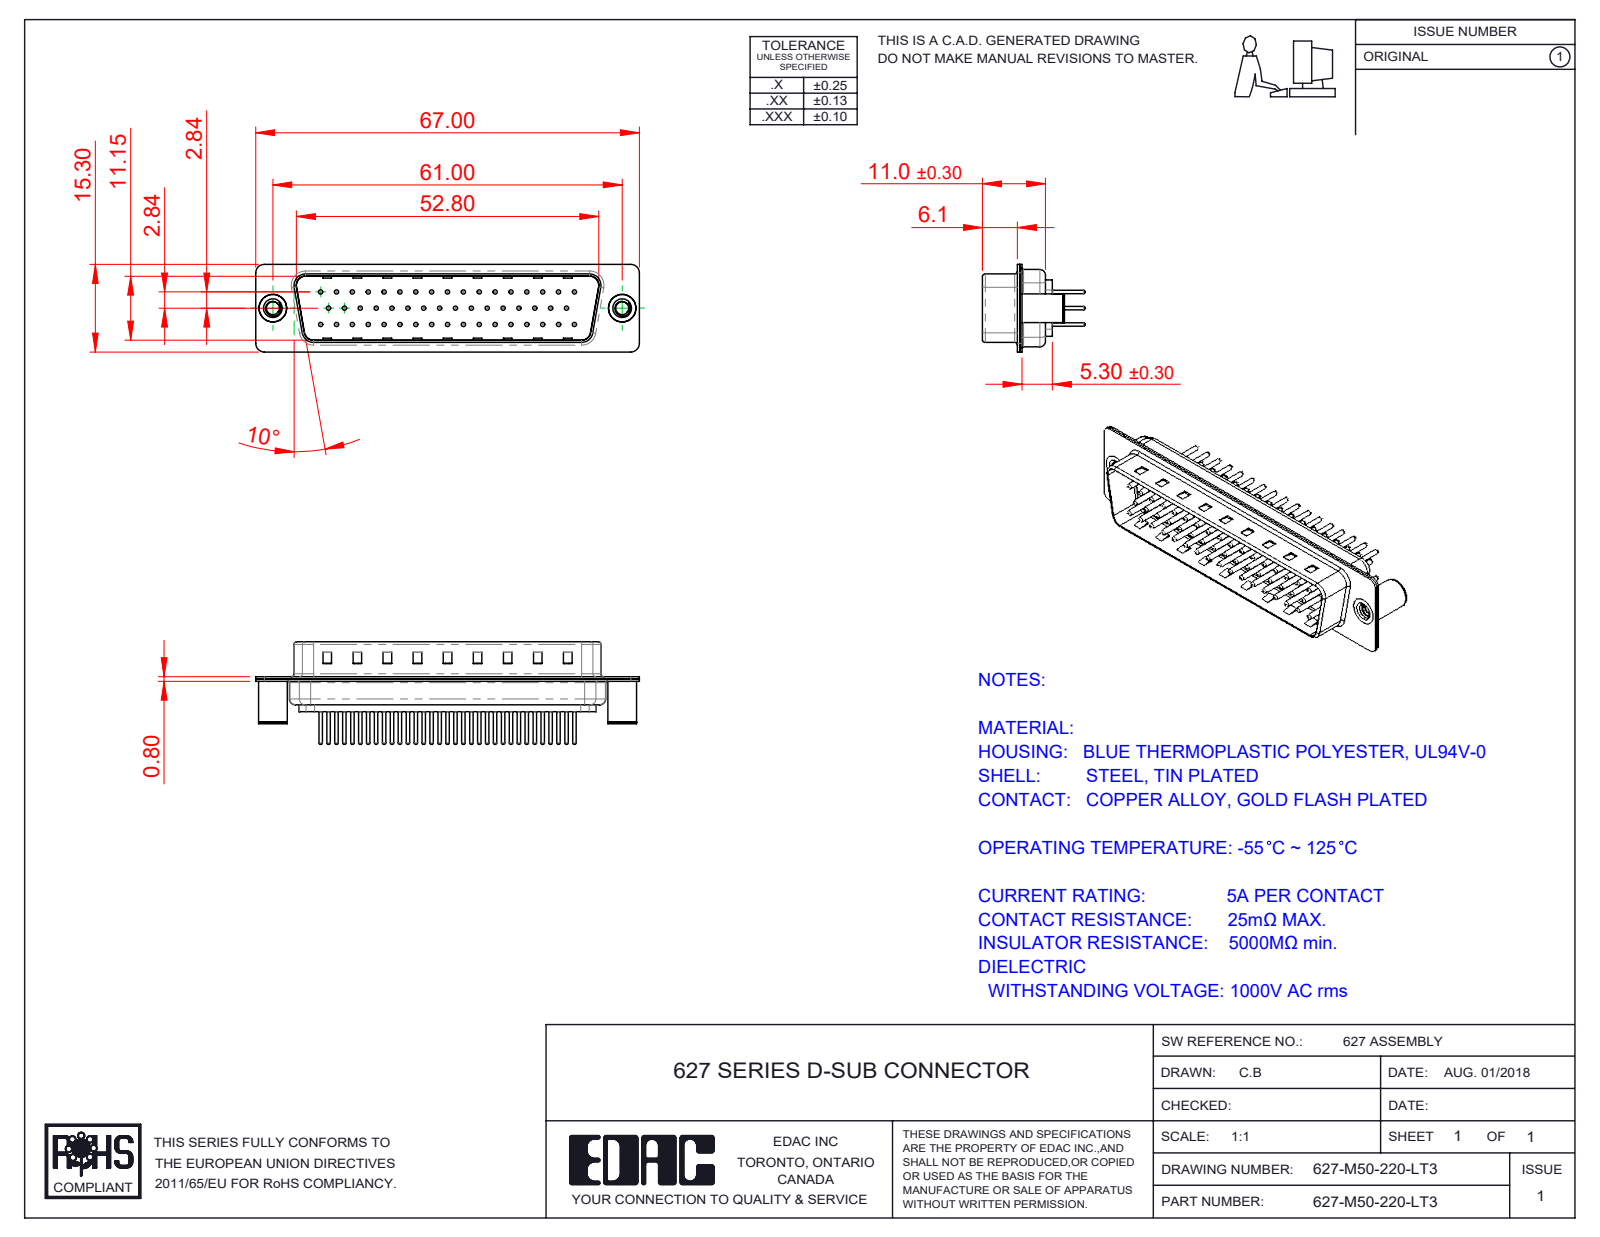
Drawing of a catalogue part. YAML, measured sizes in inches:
part_name: "627M Contact Row 3_20; 627M Shell Front_50 Contacts; 627M 4-40 Threaded Board Spacer; 627M Shell Rear_50 Contacts (+4 more)"
step_written_by: "SolidWorks 2020 (CONFIG_CONTROL_DESIGN)"
units: inches
bodies: {solids: 55, faces: 2296, planar: 553, cylindrical: 865, other: 878}
overall_size: [2.638, 0.705, 0.602]
volume: 0.284
surface_area: 16.98
round_holes:
  - {diameter: 0.03, count: 50}
  - {diameter: 0.063, count: 50}
  - {diameter: 0.079, count: 50}
  - {diameter: 0.089, count: 2}
  - {diameter: 0.128, count: 2}
  - {diameter: 0.157, count: 2}
  - {diameter: 0.189, count: 2}
round_bosses_or_shafts:
  - {diameter: 0.059, count: 50}
  - {diameter: 0.024, count: 50}
  - {diameter: 0.197, count: 2}
  - {diameter: 0.193, count: 2}
partial_cylinders:
  - {radius: 0.059, count: 16}
  - {radius: 0.079, count: 12}
  - {radius: 0.02, count: 8}
  - {radius: 0.063, count: 8}
  - {radius: 0.01, count: 4}
  - {radius: 0.024, count: 4}
  - {radius: 0.026, count: 4}
  - {radius: 0.035, count: 4}
face_to_face_distances: [0.016, 0.455, 0.224, 0.24, 0.031, 0.03, 0.485, 0.209, 0.485, 0.516]
hole_center_spacings: [0.124, 0.109, 0.218, 0.327, 0.436, 0.545, 0.654, 0.198]
